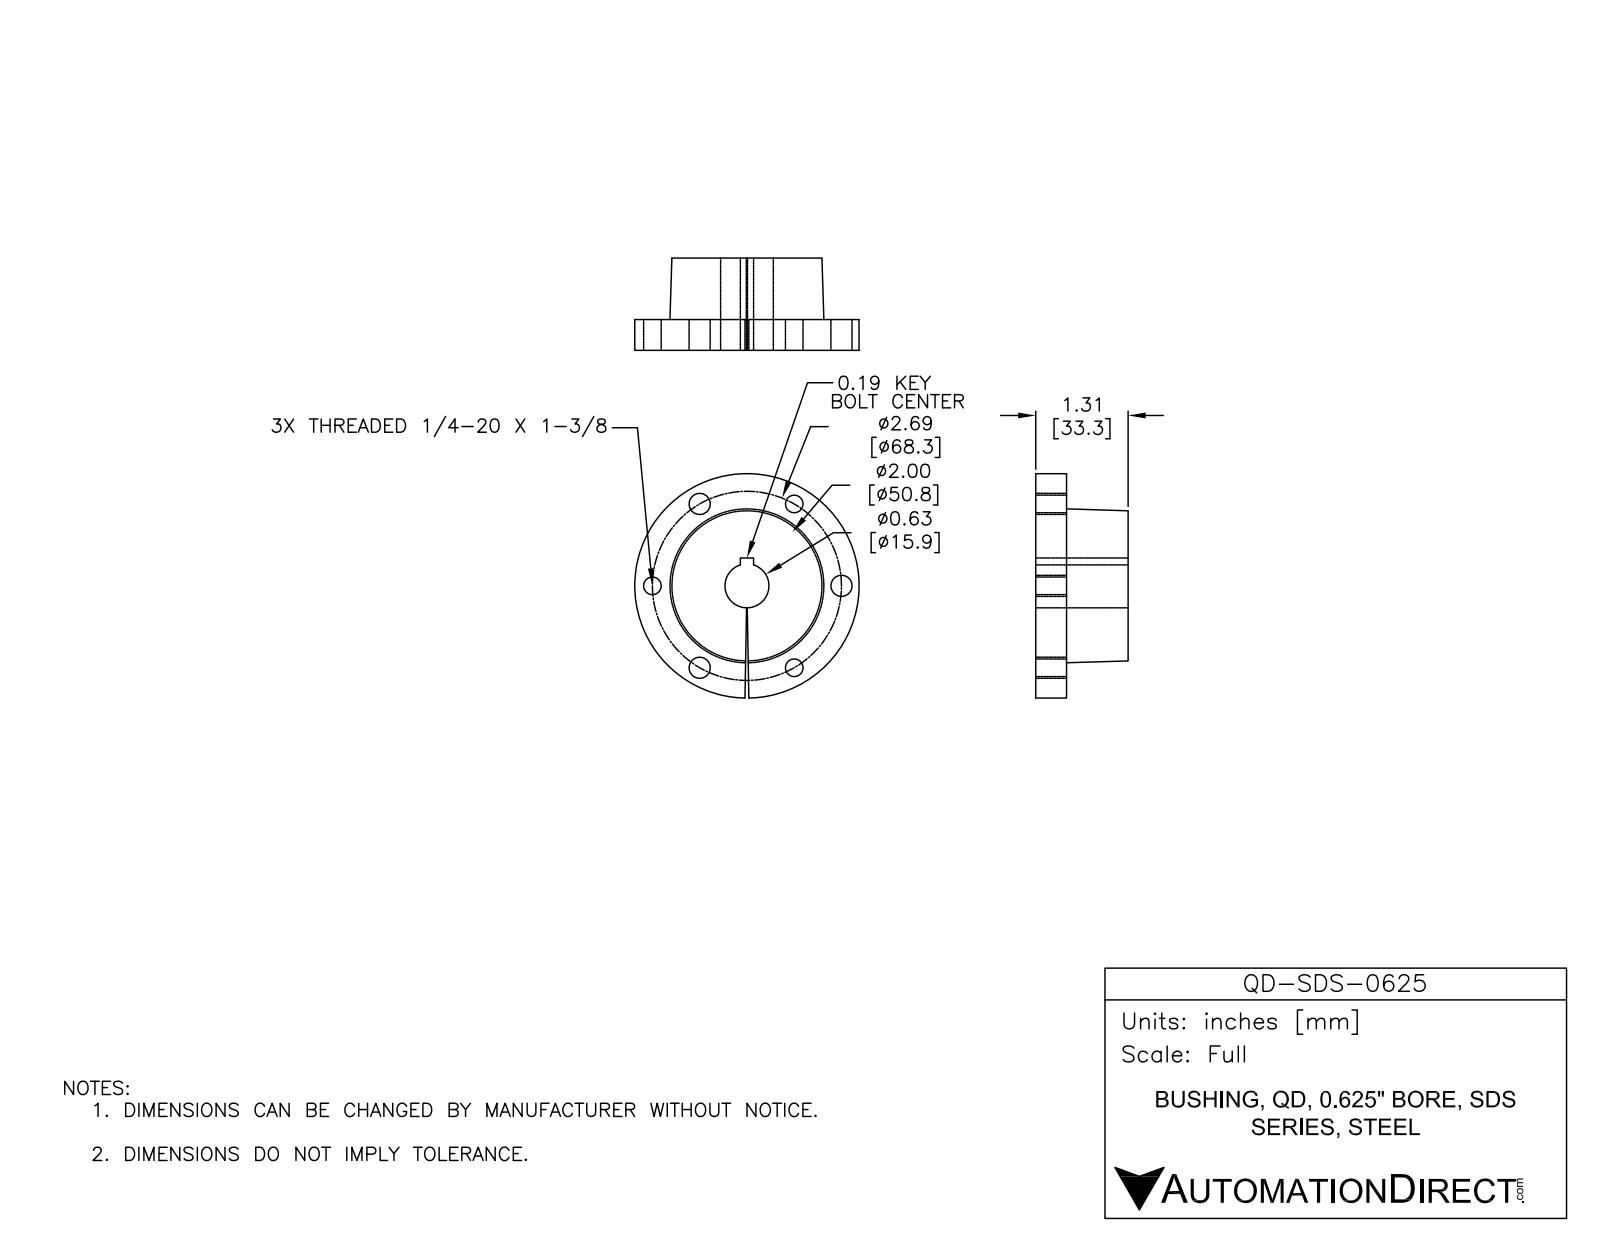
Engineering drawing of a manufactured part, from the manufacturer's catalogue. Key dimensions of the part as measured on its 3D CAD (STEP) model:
Part name (STEP PRODUCT): QD-SDS-0625
STEP written by: SolidWorks 2014 (AUTOMOTIVE_DESIGN)
Units: inches
Bodies: 1 solid, 29 faces (8 planar, 18 cylindrical, 3 other)
Overall size (bounding box): 3.188 × 3.187 × 1.313
Volume: 6.079 in³ · Surface area: 32.16 in²
Round holes (diameter × count): ⌀0.25 ×3, ⌀0.3 ×3, ⌀0.625 ×1
Round bosses / shafts (diameter × count): ⌀3.187 ×1
Main face-to-face distances: 0.437, 1.313, 0.875, 0.187
Hole centre spacings: 1.344, 2.328, 1.344, 2.688, 2.687
